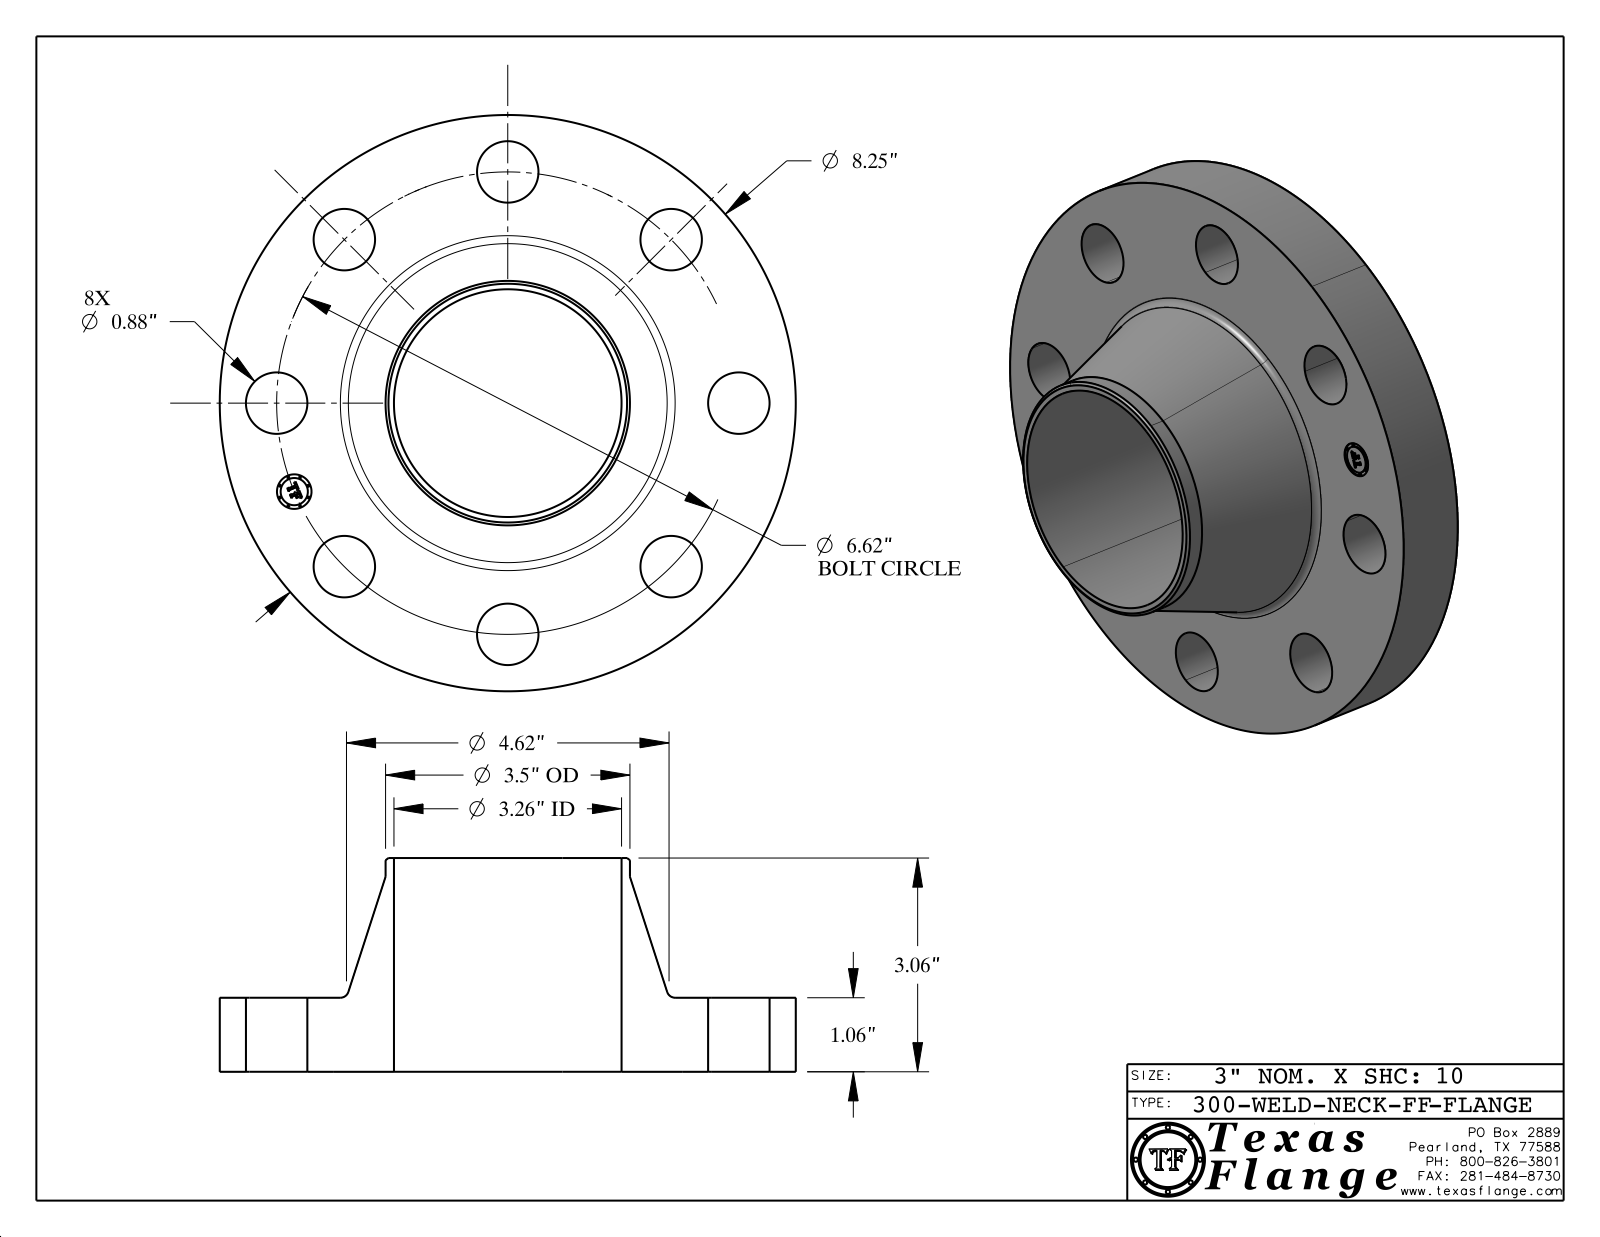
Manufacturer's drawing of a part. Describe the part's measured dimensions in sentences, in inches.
The part is named "300-WELD-NECK-FF". Its 3-D file was written by "CATIA V5 STEP AP214 (AUTOMOTIVE_DESIGN)". It is 1 solid with 417 faces: 369 planar, 42 cylindrical and 6 other. Overall it measures 8.25 by 8.25 by 3.06 inches. Its volume is 51.12 cubic inches and its surface area 181.3 square inches. Round holes: 8 of diameter 0.88, 1 of diameter 0.495, 1 of diameter 3.26. Round bosses or shafts: 8 of diameter 0.03, 1 of diameter 8.25, 1 of diameter 3.5, 1 of diameter 0.39. The main face-to-face distances are 1.06, 3.06, 2, 0.015, 1.045, 2.015, 0.148, 0.145, 0.027, 0.096. The hole center spacings are 3.31, 2.533, 6.116, 4.681, 4.681, 1.291, 3.678, 6.493.
